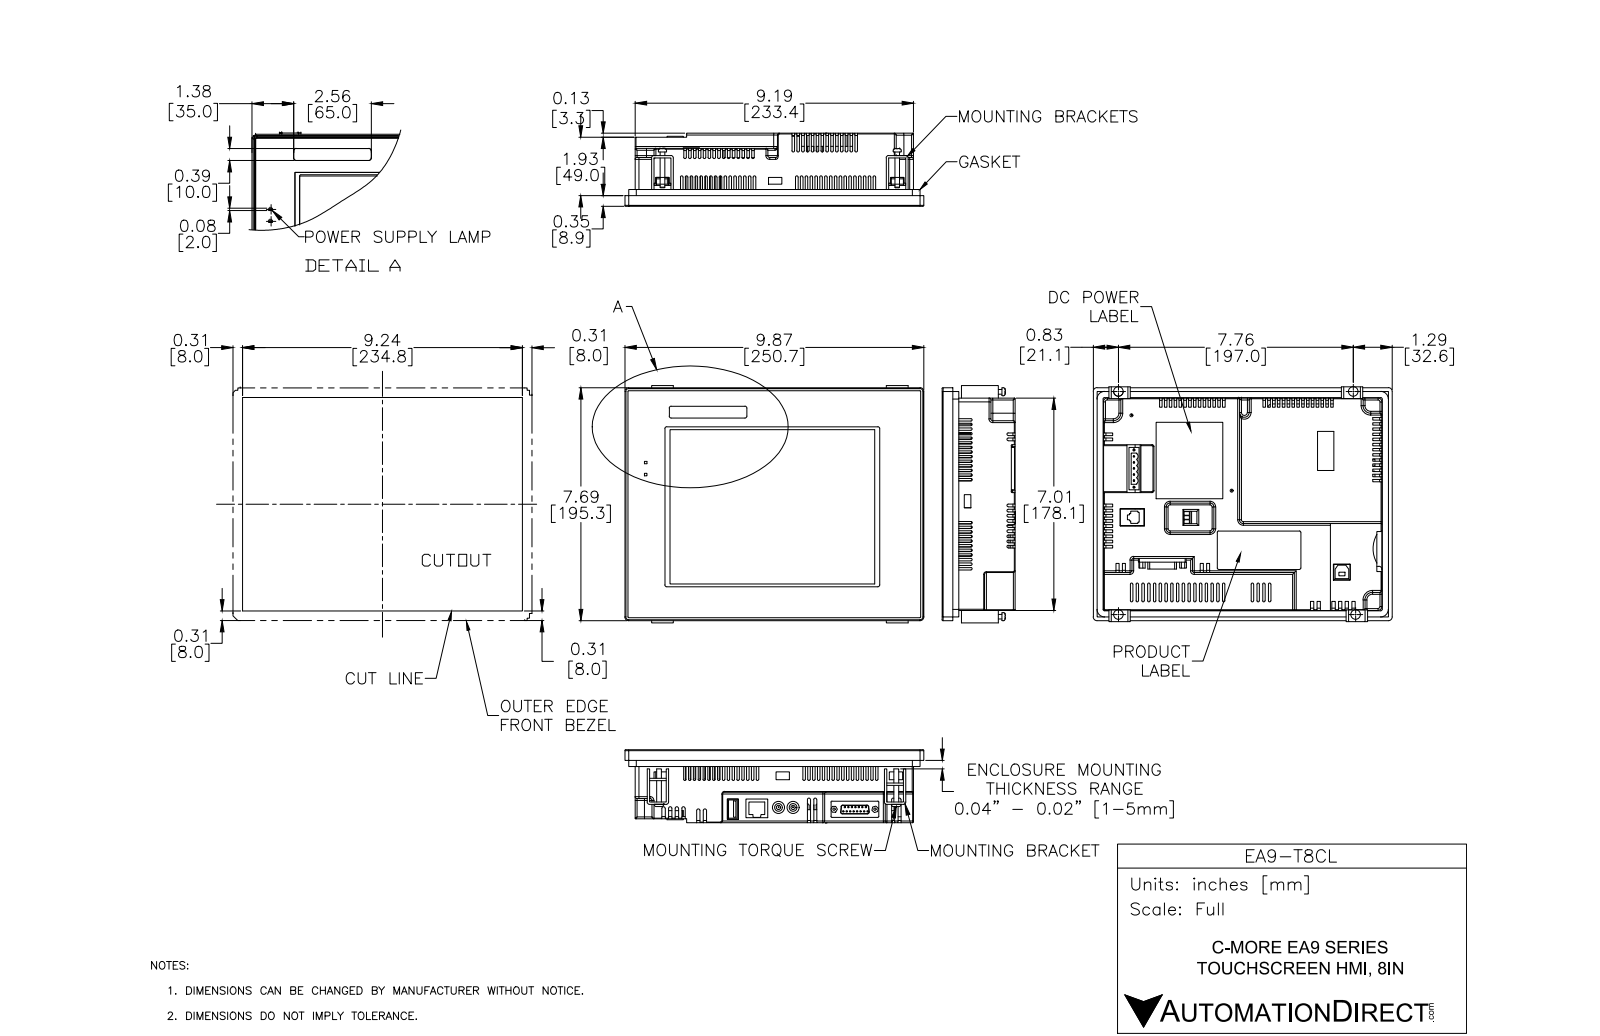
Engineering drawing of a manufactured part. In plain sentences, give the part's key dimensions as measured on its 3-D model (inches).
The part is named "EA9-T8CL". Its 3-D file was written by "SolidWorks 2014 (AUTOMOTIVE_DESIGN)". It is 8 solids with 1754 faces: 936 planar, 762 cylindrical and 56 other. Overall it measures 9.87 by 7.69 by 2.418 inches. Its volume is 31.08 cubic inches and its surface area 511.9 square inches. Round holes: 14 of diameter 0.045, 2 of diameter 0.07, 2 of diameter 0.08, 2 of diameter 0.103, 2 of diameter 0.14, 2 of diameter 0.4, 1 of diameter 0.045. Round bosses or shafts: 5 of diameter 0.05, 2 of diameter 0.25. Partial cylindrical surfaces (rounded edges, fillets, slot ends): 198 of radius 0.04, 92 of radius 0.042, 30 of radius 0.06, 21 of radius 0.063, 20 of radius 0.041, 19 of radius 0.062, 18 of radius 0.025, 15 of radius 0.045. The main face-to-face distances are 0.075, 0.075, 2.334, 0.5, 1.834, 2.333, 2.409, 2.335, 2.259, 2.259. The hole center spacings are 0.115, 0.15, 0.152, 0.224, 0.229, 0.343, 0.458, 0.229.
